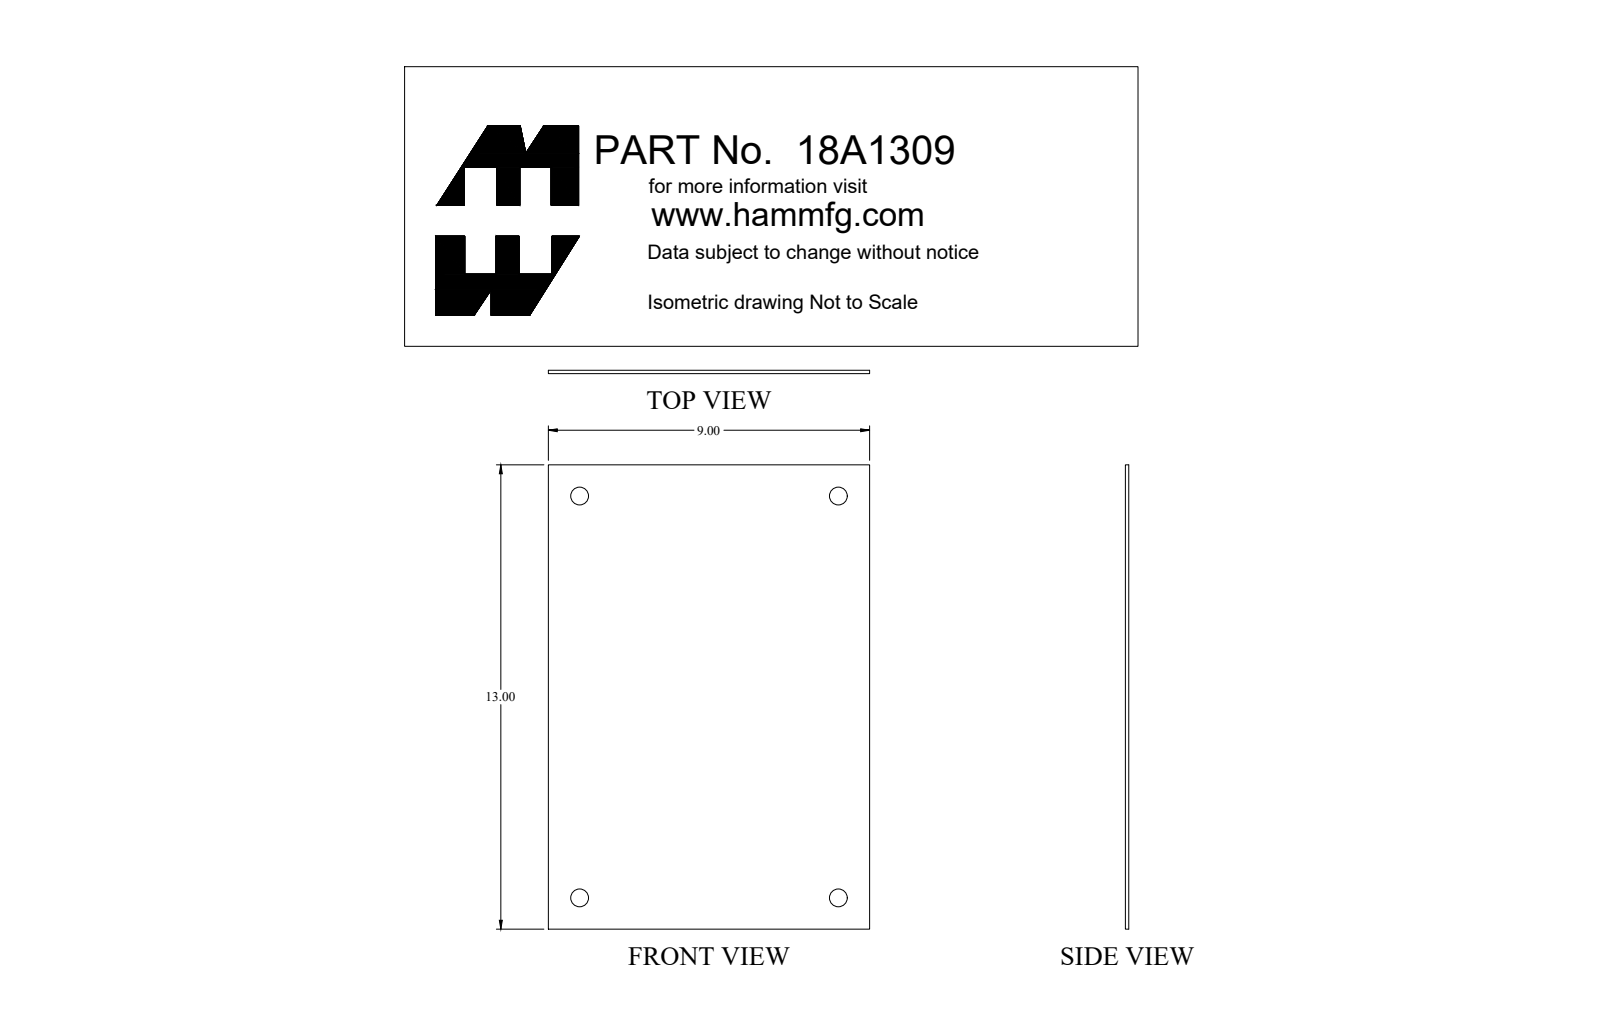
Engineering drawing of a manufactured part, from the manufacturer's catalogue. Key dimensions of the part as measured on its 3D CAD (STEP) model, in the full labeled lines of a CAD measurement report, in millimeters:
Part name (STEP PRODUCT): 18A1309
STEP written by: SolidWorks 2018 (AUTOMOTIVE_DESIGN)
Units: millimetres
Bodies: 1 solid, 10 faces (6 planar, 4 cylindrical, 0 other)
Overall size (bounding box): 330.2 × 228.6 × 2.4
Volume: 180 900 mm³ · Surface area: 153 000 mm²
Round holes (diameter × count): ⌀12.7 ×4
Main face-to-face distances: 2.4, 228.6, 330.2
Hole centre spacings: 184.2, 285.8, 340
